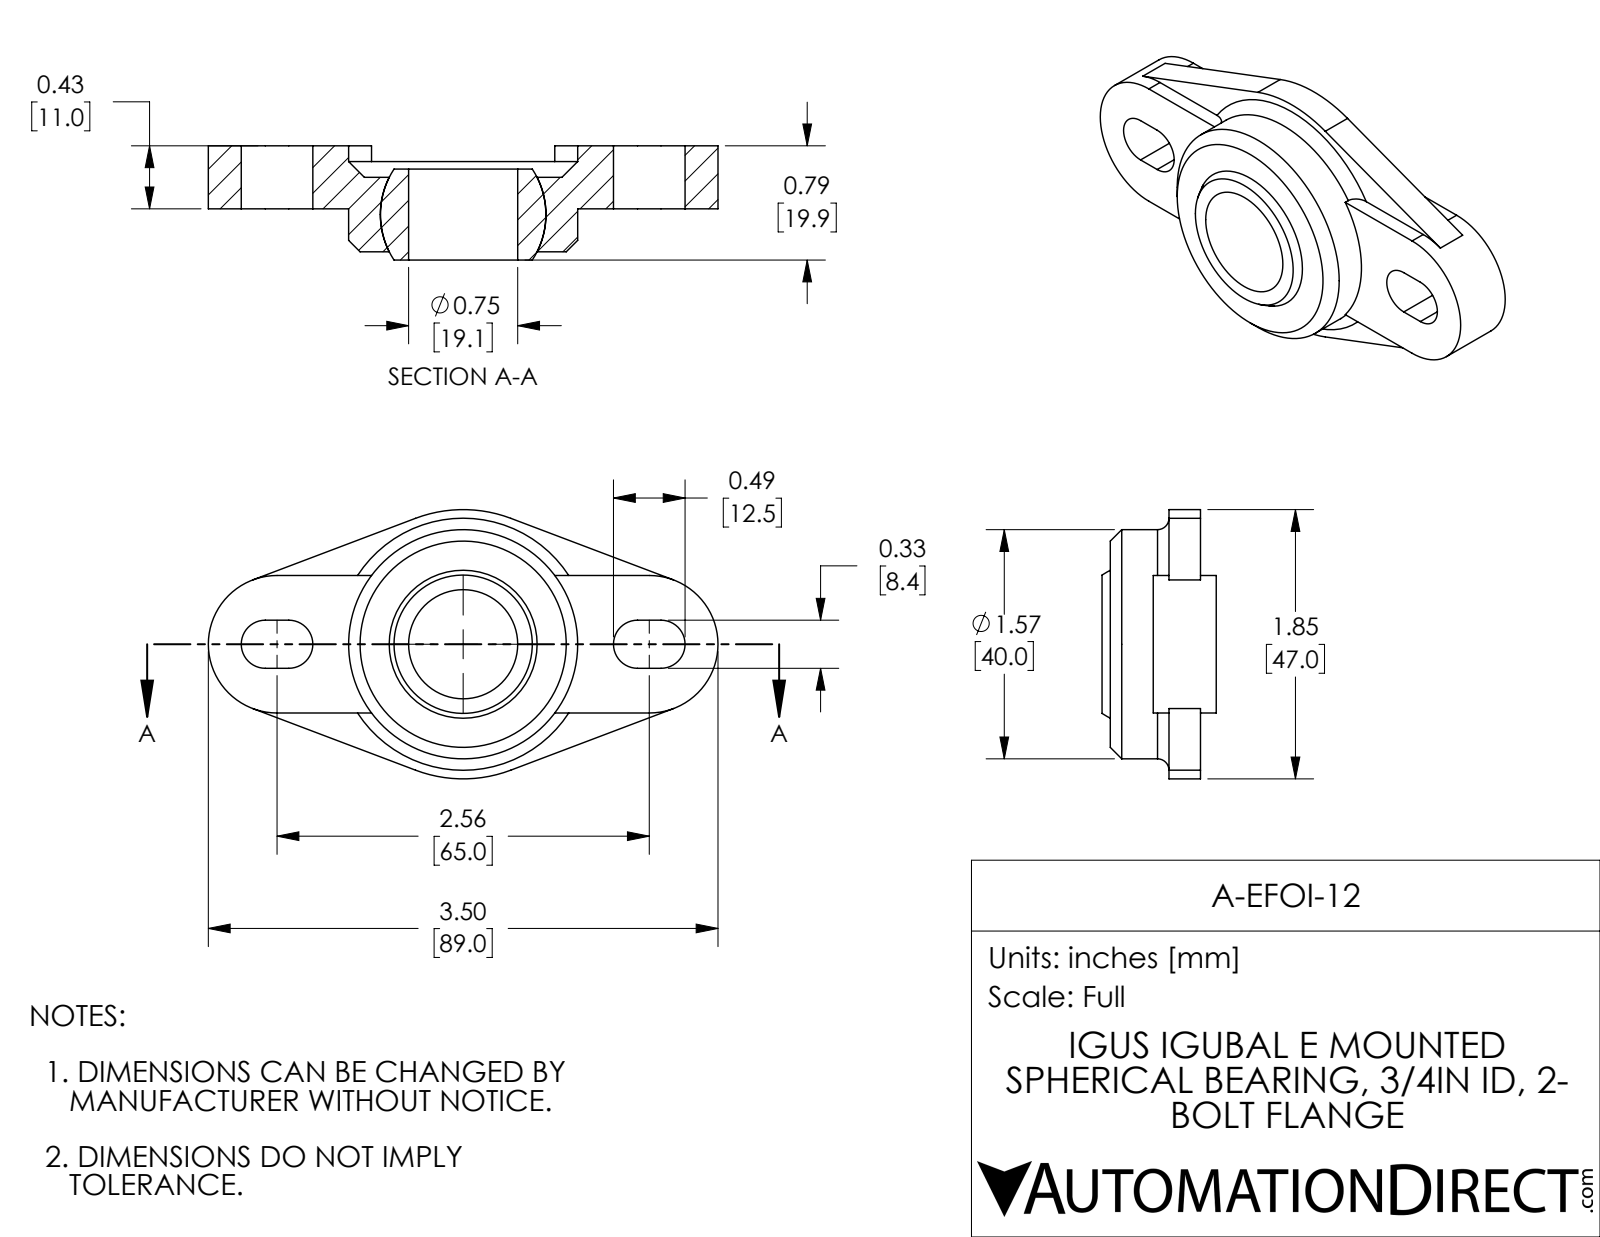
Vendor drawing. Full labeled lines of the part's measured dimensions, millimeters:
Part name (STEP PRODUCT): A-EFOI-12
STEP written by: SolidWorks 2017 (AUTOMOTIVE_DESIGN)
Units: millimetres
Bodies: 2 solids, 56 faces (28 planar, 18 cylindrical, 10 other)
Overall size (bounding box): 89 × 47 × 25.9
Volume: 26 710 mm³ · Surface area: 12 240 mm²
Round holes (diameter × count): ⌀19.1 ×1, ⌀40 ×1
Partial cylindrical surfaces — rounded edges, fillets, slot ends (radius × count): R4.2 ×4, R12 ×2, R23.5 ×1
Main face-to-face distances: 2.7, 5.5, 11, 8.3, 18.5, 15.7, 7.5, 13, 10.3, 1.4
